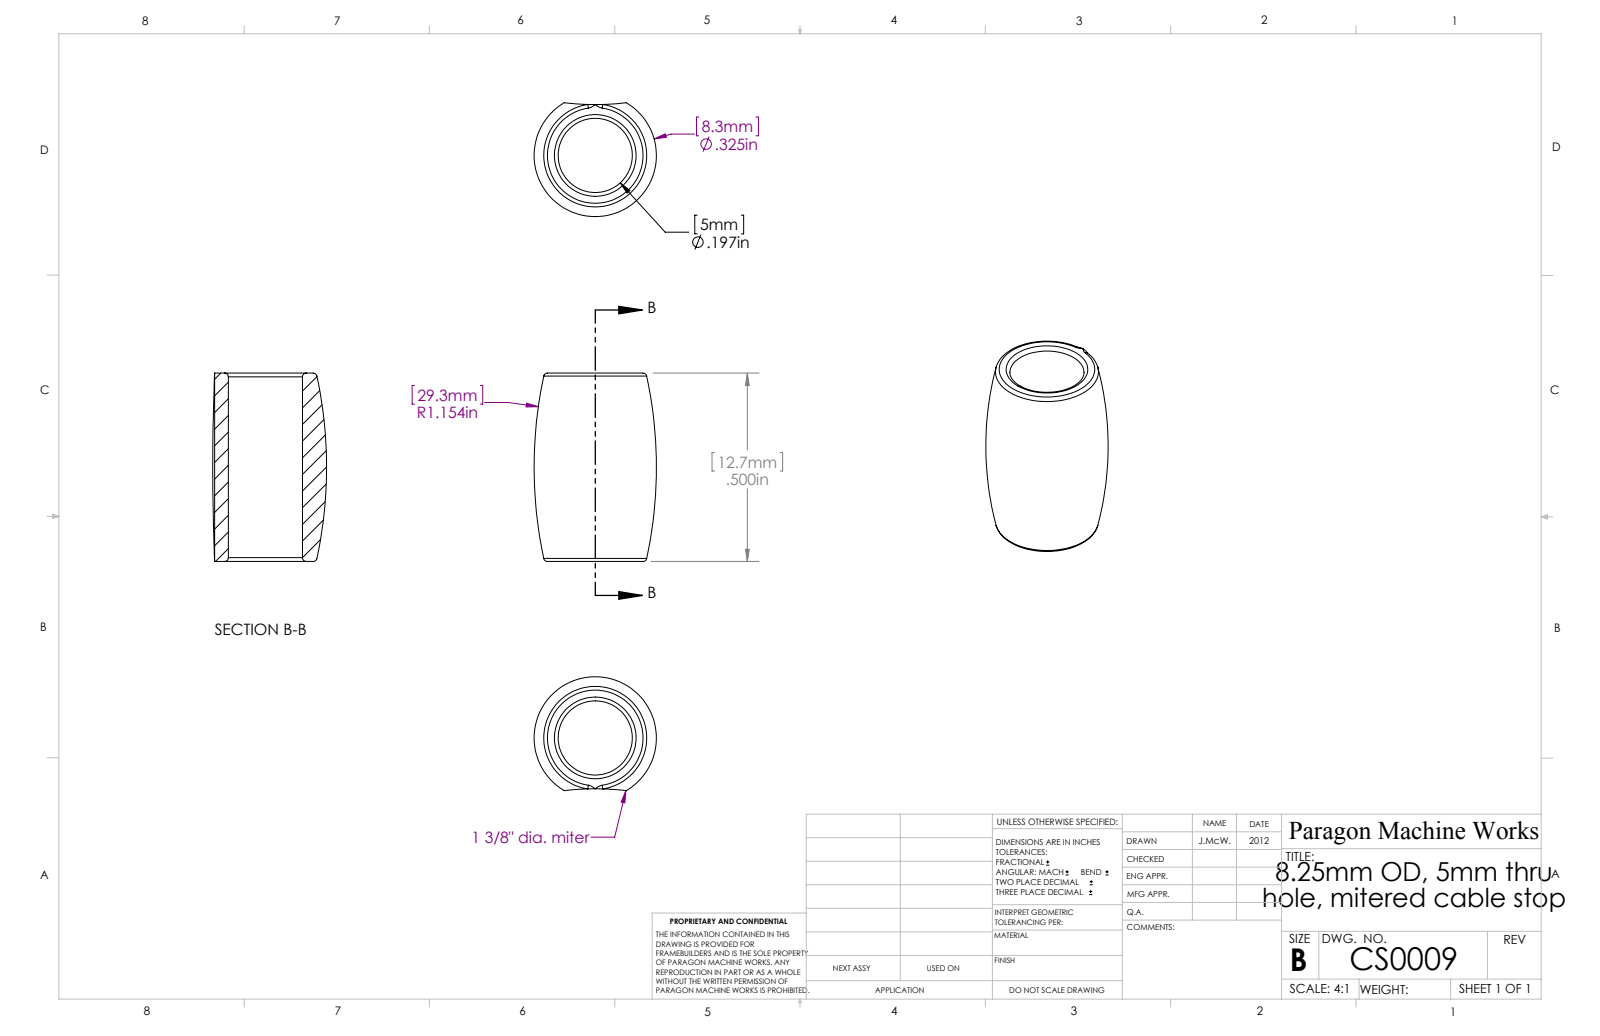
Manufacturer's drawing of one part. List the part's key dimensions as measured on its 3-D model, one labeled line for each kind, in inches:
Part name (STEP PRODUCT): CS0009
STEP written by: SolidWorks 2012 (AUTOMOTIVE_DESIGN)
Units: inches
Bodies: 1 solid, 13 faces (2 planar, 2 cylindrical, 9 other)
Overall size (bounding box): 0.5 × 0.325 × 0.302
Volume: 0.021 in³ · Surface area: 0.836 in²
Round holes (diameter × count): ⌀0.197 ×1
Partial cylindrical surfaces — rounded edges, fillets, slot ends (radius × count): R0.687 ×1
Main face-to-face distances: 0.5
